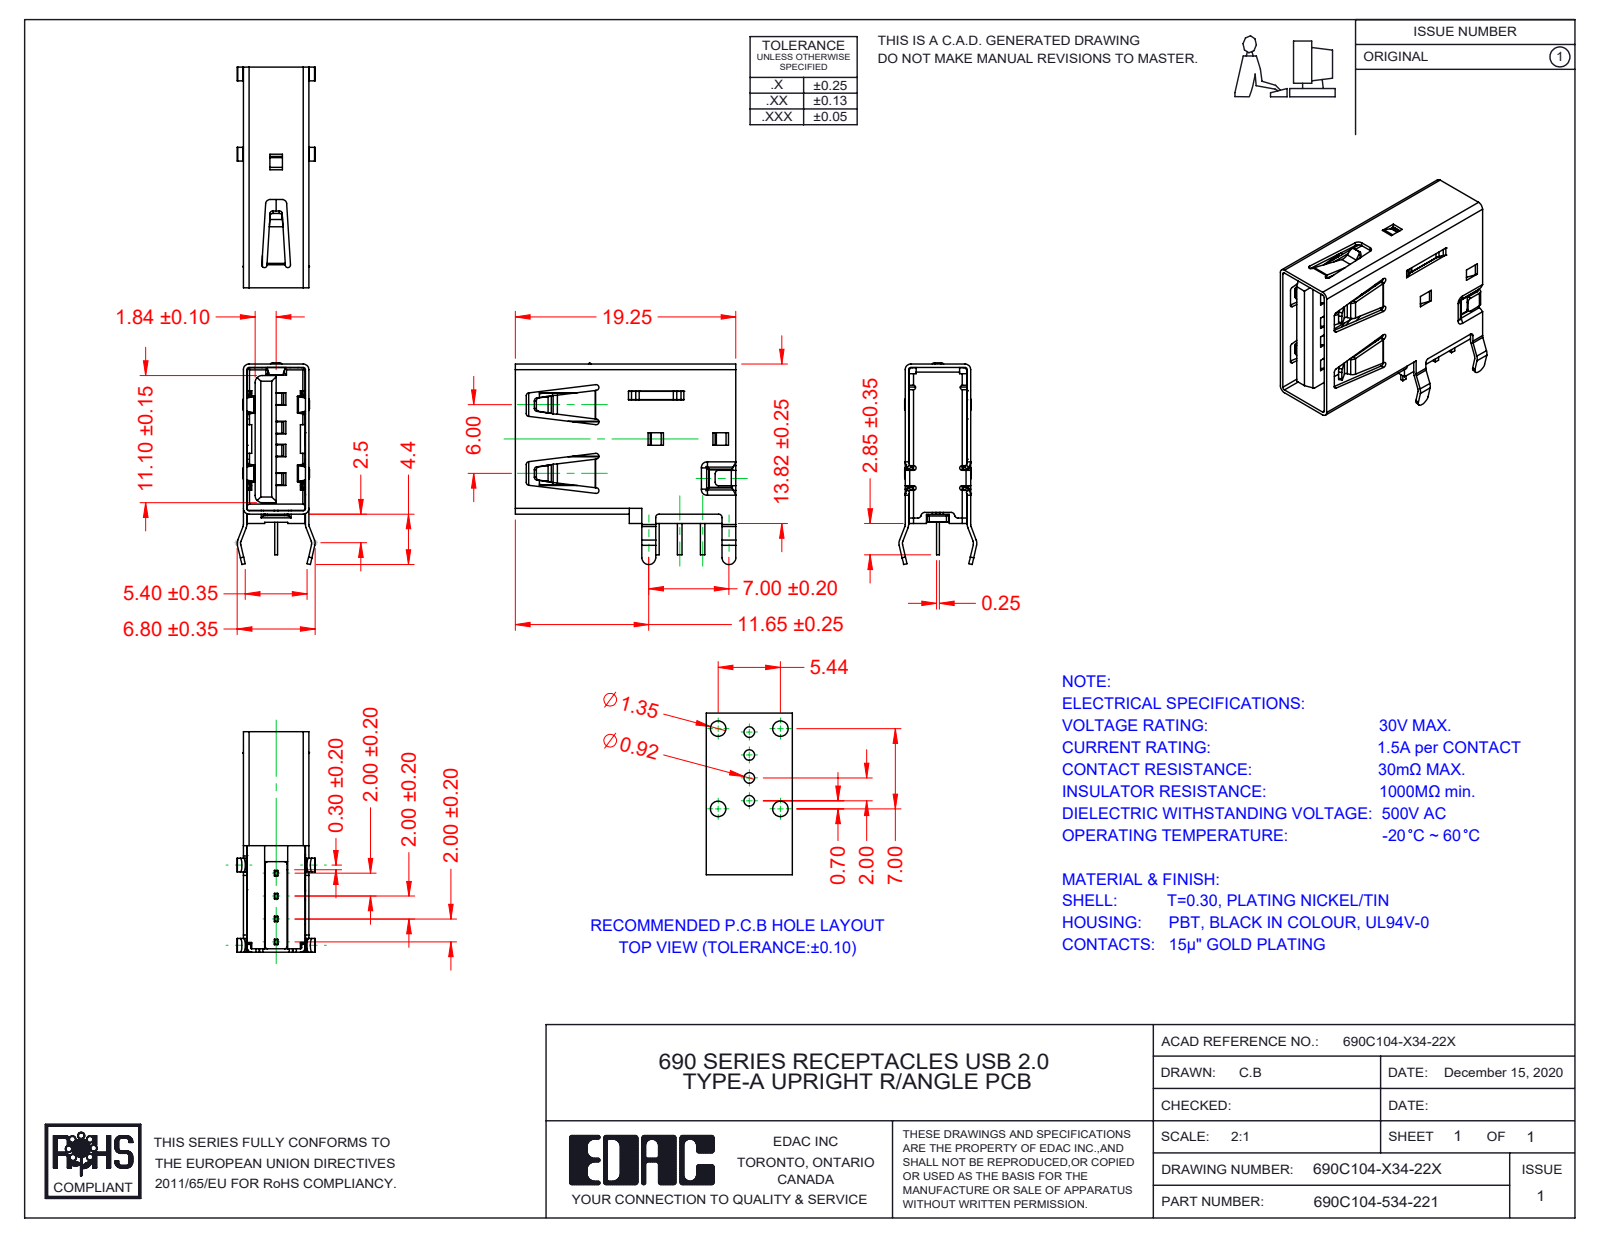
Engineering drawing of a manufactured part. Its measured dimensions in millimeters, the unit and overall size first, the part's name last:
Units: millimetres
Overall size (bounding box): 19.25 × 17.61 × 6.8
Partial cylindrical surfaces — rounded edges, fillets, slot ends (radius × count): R0.3 ×42, R0.4 ×24, R0.6 ×24, R0.25 ×23, R0.2 ×21, R0.15 ×18, R0.1 ×15, R0.5 ×11
Main face-to-face distances: 5.42, 5.12, 5.72, 12.8, 2.5, 2.52, 5.38, 2.86, 2.56, 4.7
Volume: 658 mm³ · Surface area: 2 729 mm²
Bodies: 8 solids, 1166 faces (753 planar, 317 cylindrical, 96 other)
Part name (STEP PRODUCT): Shell 690C104-X34-22X; Contact1 690C104-X34-22X; Contact4 690C104-X34-22X; 690C104-134-221 (+6 more)
STEP written by: SolidWorks 2020 (AUTOMOTIVE_DESIGN)
